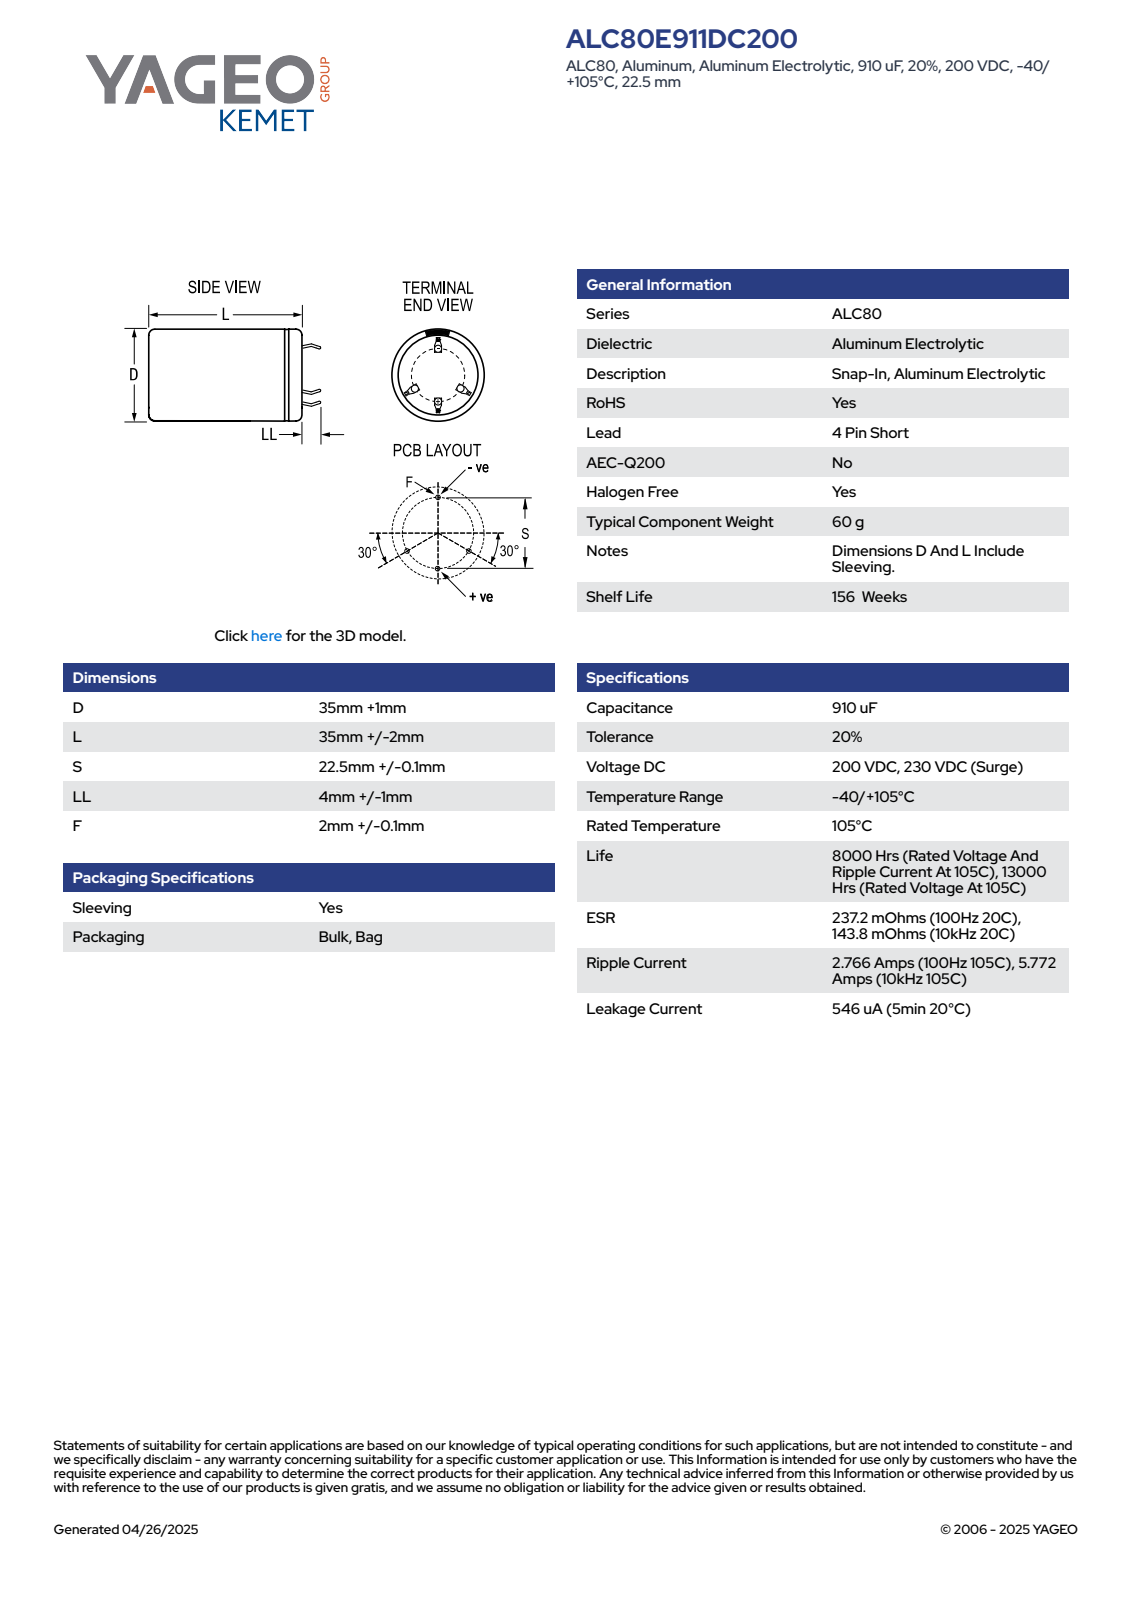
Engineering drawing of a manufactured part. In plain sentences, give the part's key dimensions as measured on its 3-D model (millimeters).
The part is named "CARS_K4P_35X35_D36L37S22.5LL5F2.1". Its 3-D file was written by "SolidWorks 2014 (AUTOMOTIVE_DESIGN)". It is 1 solid with 134 faces: 80 planar, 15 cylindrical and 39 other. Overall it measures 41.99 by 36 by 36 millimeters. Its volume is 37 143 cubic millimeters and its surface area 6 243 square millimeters. Round holes: 1 of diameter 31.85. Round bosses or shafts: 1 of diameter 36. Partial cylindrical surfaces (rounded edges, fillets, slot ends): 1 of radius 17.99. The main face-to-face distances are 36.99, 37.49, 0.5, 0.6, 0.55, 0.75, 1.35, 22.42, 2.1, 21.87.
